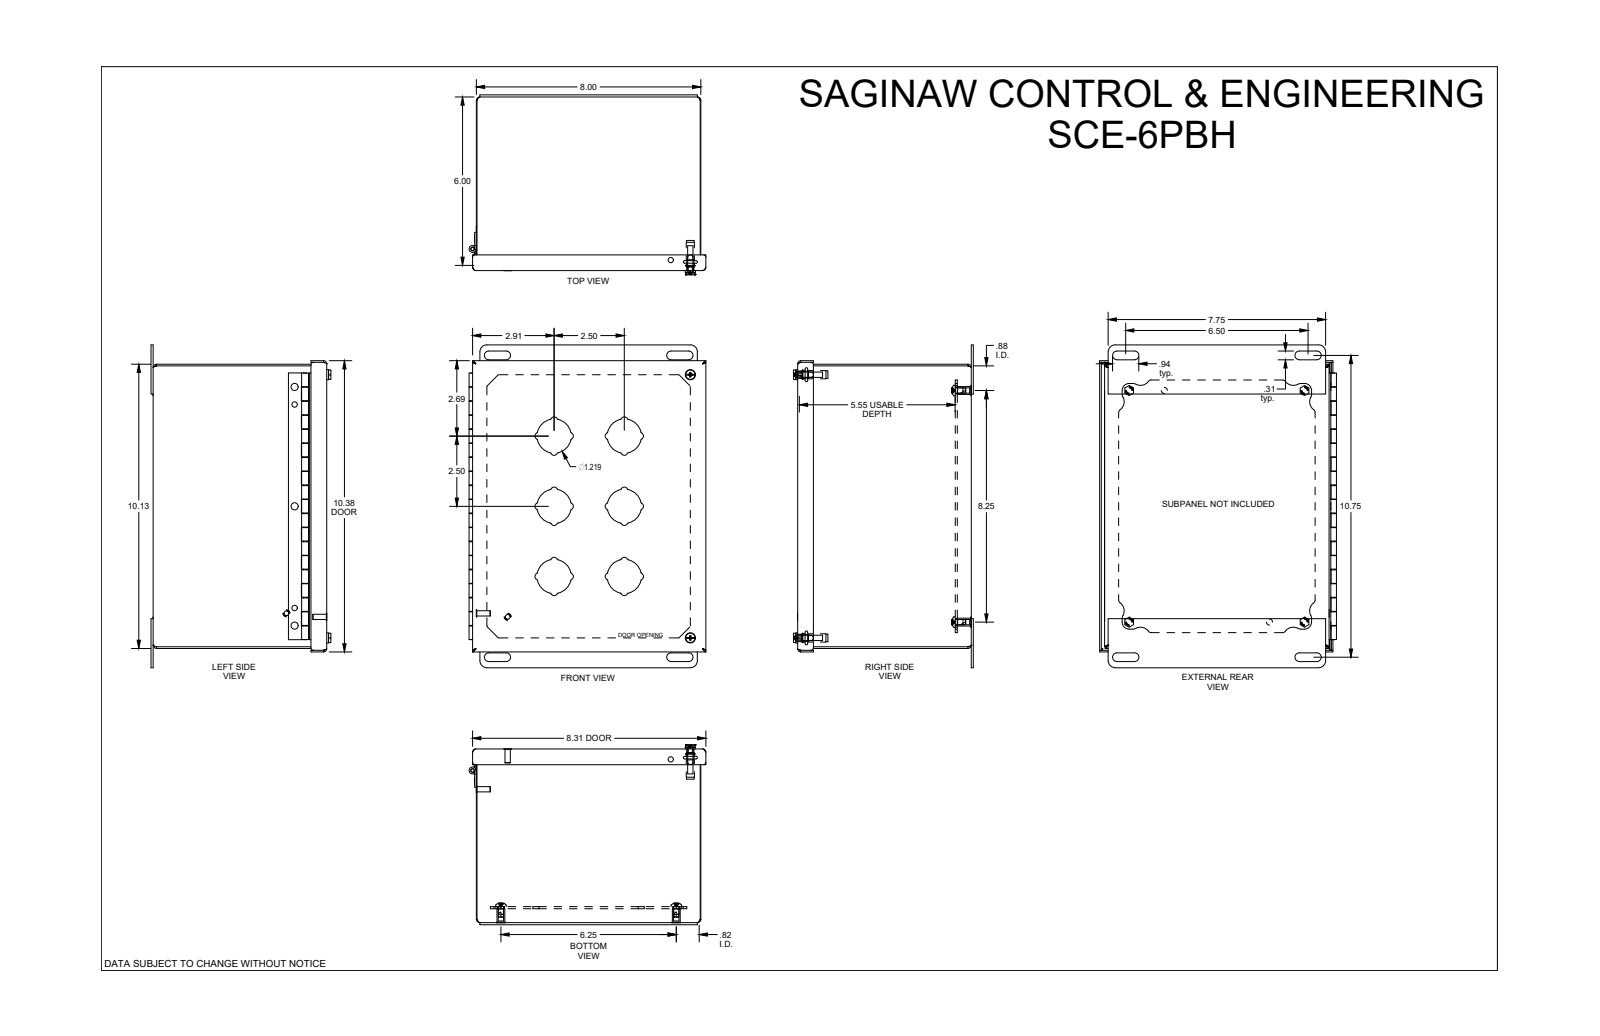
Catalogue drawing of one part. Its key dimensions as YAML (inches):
part_name: "SCE-6PBH"
step_written_by: "SolidWorks 2021 (AUTOMOTIVE_DESIGN)"
units: inches
bodies: {solids: 7, faces: 915, planar: 362, cylindrical: 383, other: 170}
overall_size: [11.5, 9.124, 6.323]
round_holes:
  - {diameter: 0.19, count: 9}
  - {diameter: 0.25, count: 6}
  - {diameter: 0.266, count: 4}
  - {diameter: 0.317, count: 4}
  - {diameter: 0.193, count: 2}
  - {diameter: 0.218, count: 2}
  - {diameter: 0.22, count: 2}
  - {diameter: 0.126, count: 1}
round_bosses_or_shafts:
  - {diameter: 0.188, count: 5}
  - {diameter: 0.28, count: 4}
  - {diameter: 0.256, count: 4}
  - {diameter: 0.362, count: 2}
  - {diameter: 0.292, count: 2}
  - {diameter: 0.27, count: 2}
  - {diameter: 0.26, count: 2}
  - {diameter: 0.246, count: 1}
partial_cylinders:
  - {radius: 0.04, count: 48}
  - {radius: 0.125, count: 32}
  - {radius: 0.06, count: 20}
  - {radius: 0.01, count: 18}
  - {radius: 0.25, count: 16}
  - {radius: 0.156, count: 8}
  - {radius: 0.344, count: 8}
  - {radius: 0.2, count: 6}
face_to_face_distances: [0.06, 6.125, 7.94, 10.065, 6.065, 6.185, 0.075, 0.51, 0.495, 0.435]
hole_center_spacings: [0.753, 7.25, 6.773, 7.229, 8.827, 10.35, 0.037, 1.839]
